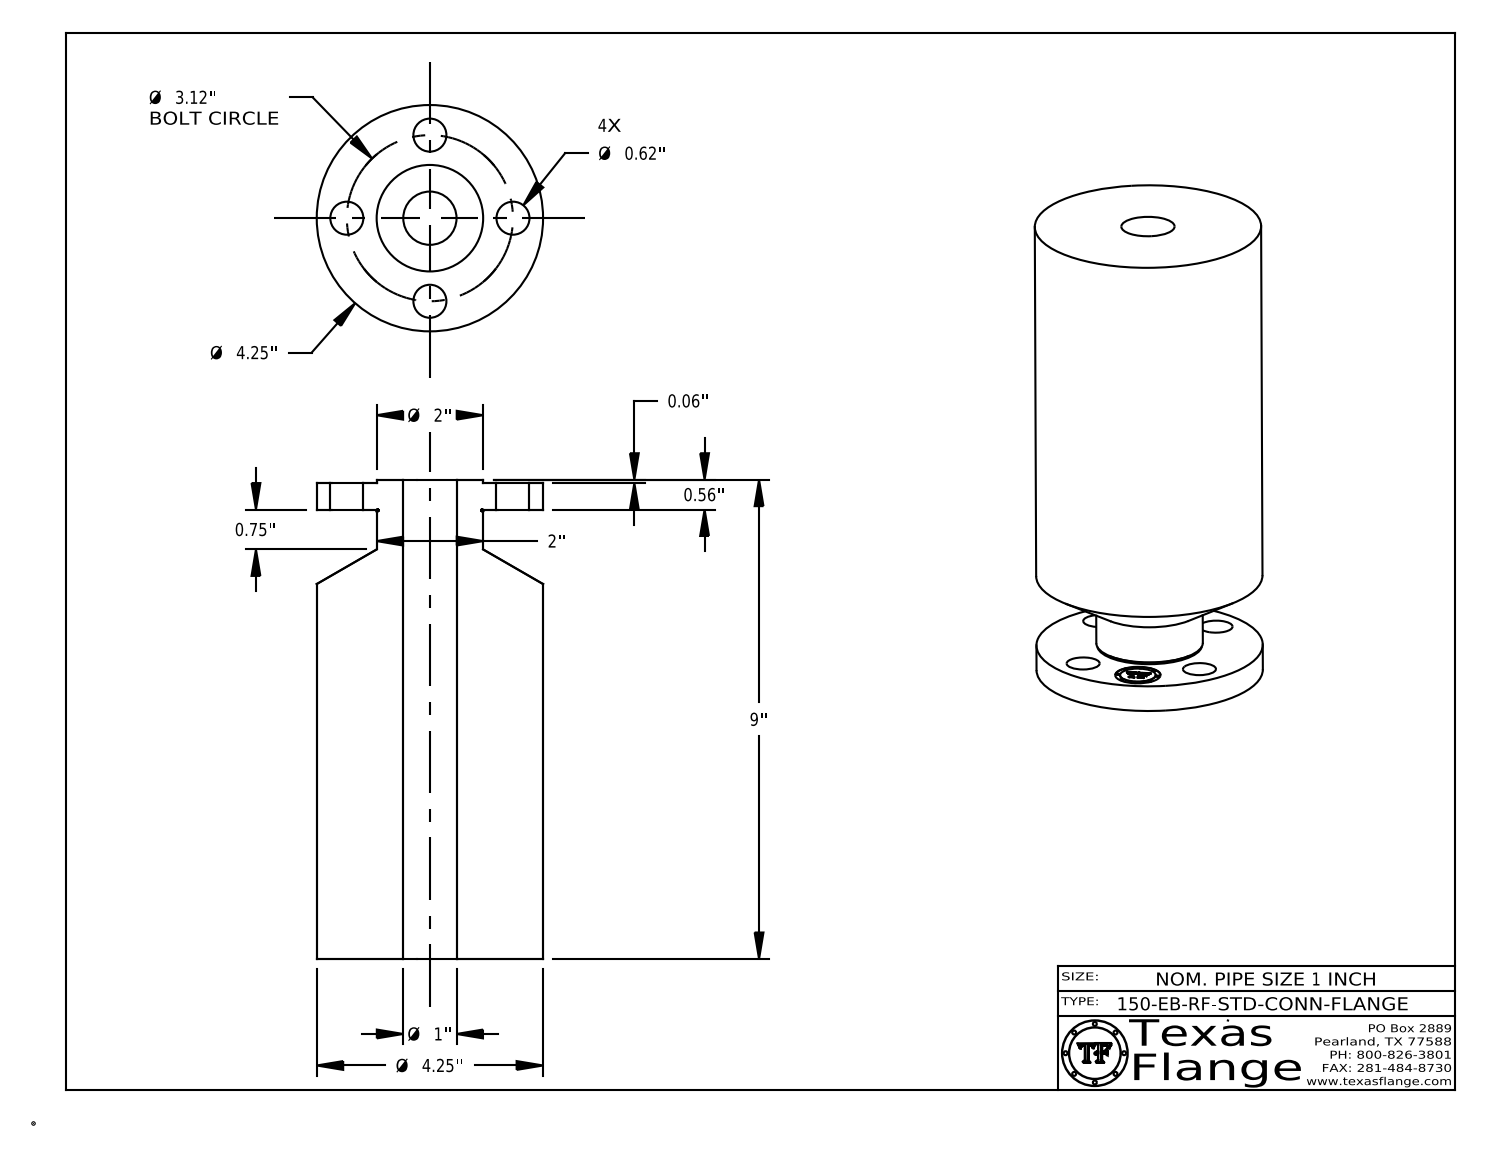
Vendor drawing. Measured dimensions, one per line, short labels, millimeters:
name: 1-150-EB-RF-STD-CONN-FLANGE
written by: CATIA V5 STEP AP214 (AUTOMOTIVE_DESIGN)
unit: mm
bodies: 1 solid, 413 faces (369 planar, 38 cylindrical, 6 other)
size: 228.6 × 108 × 108
volume: 1 753 000 mm³; area: 120 300 mm²
holes: 4× ⌀15.7, 1× ⌀21.6, 1× ⌀25.4
bosses: 8× ⌀1.3, 1× ⌀108, 1× ⌀50.8, 1× ⌀17
face distances: 227, 12.6, 214.4, 1.6, 14.2, 228.6, 14.1, 12.5, 214.5, 6.5
hole spacings: 39.6, 56, 30.3, 73.2, 79.2, 39.6
